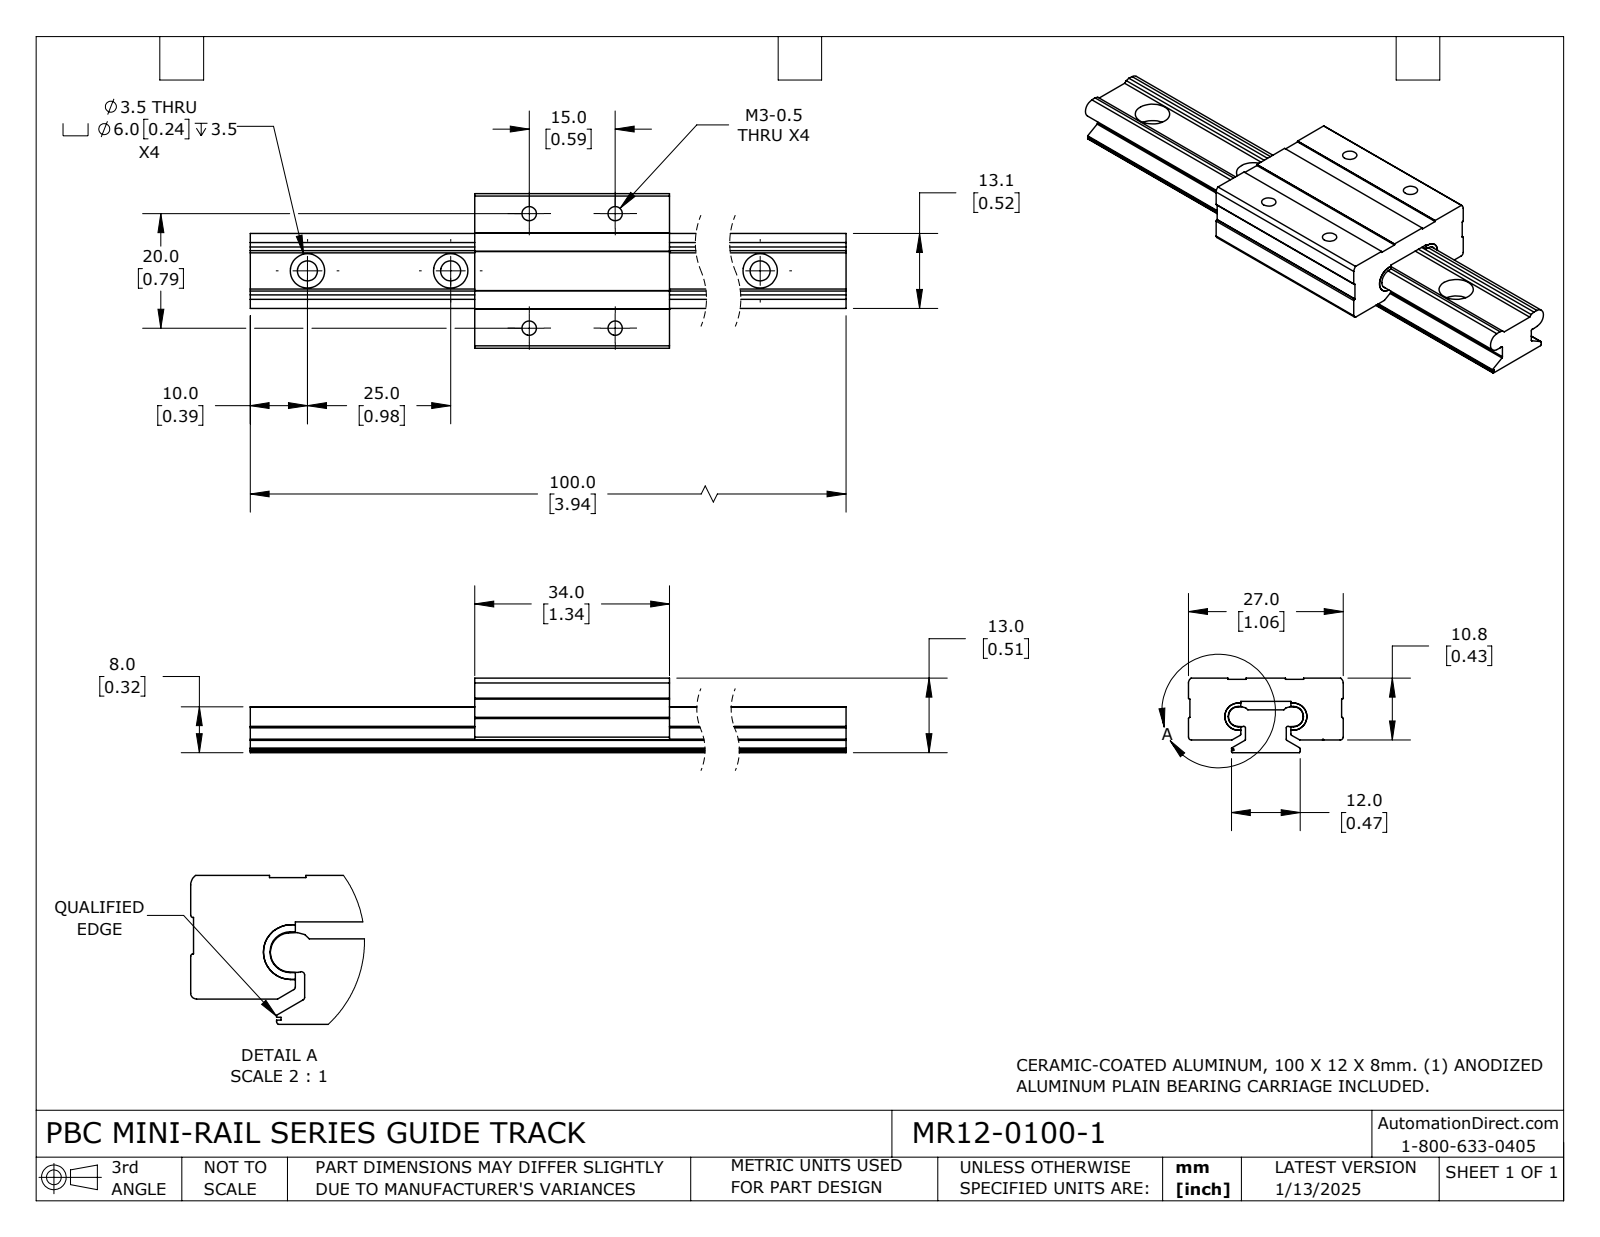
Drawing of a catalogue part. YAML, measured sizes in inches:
part_name: "MR12-0100-1_CARRIAGE; MR12-0100-1; MR12-0100-1_RAILS"
step_written_by: "SolidWorks 2023 (CONFIG_CONTROL_DESIGN)"
units: inches
bodies: {solids: 4, faces: 147, planar: 87, cylindrical: 60, other: 0}
overall_size: [3.937, 1.063, 0.512]
volume: 0.877
surface_area: 16.01
round_holes:
  - {diameter: 0.098, count: 4}
  - {diameter: 0.138, count: 4}
  - {diameter: 0.236, count: 4}
partial_cylinders:
  - {radius: 0.01, count: 9}
  - {radius: 0.008, count: 8}
  - {radius: 0.069, count: 4}
  - {radius: 0.011, count: 2}
  - {radius: 0.02, count: 2}
  - {radius: 0.04, count: 2}
  - {radius: 0.067, count: 2}
  - {radius: 0.094, count: 2}
face_to_face_distances: [0.512, 0.293, 0.219, 0.087, 0.206, 0.425, 0.391, 0.672, 0.352, 0.265]
hole_center_spacings: [0.984, 0.42, 0.591, 0.593, 0.668, 0.787, 0.925, 0.984]
